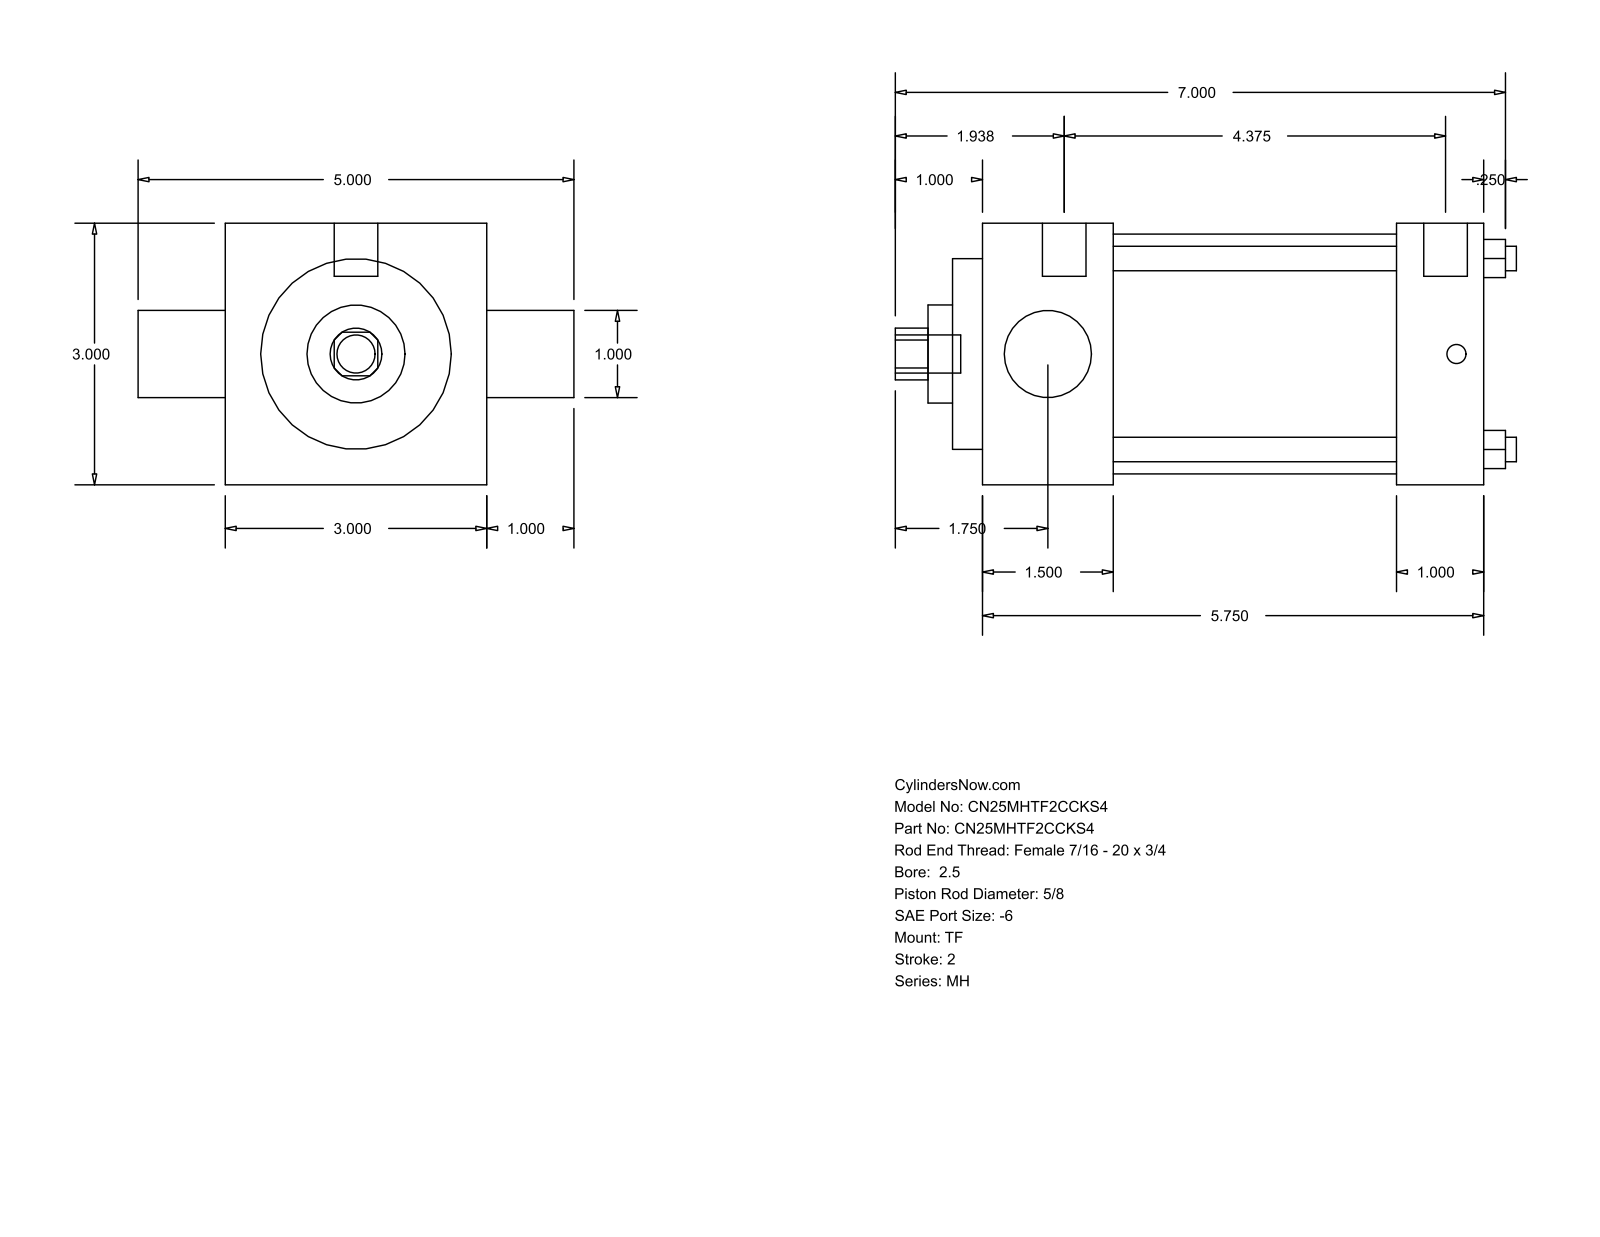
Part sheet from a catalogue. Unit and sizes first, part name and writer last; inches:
Units: inches
Overall size (bounding box): 7.125 × 5 × 3
Round holes (diameter × count): ⌀0.281 ×4, ⌀0.625 ×1, ⌀1 ×1, ⌀1.125 ×1, ⌀2.187 ×1, ⌀2.75 ×1
Round bosses / shafts (diameter × count): ⌀0.219 ×3, ⌀0.5 ×2, ⌀0.437 ×1
Partial cylindrical surfaces — rounded edges, fillets, slot ends (radius × count): R0.297 ×1
Main face-to-face distances: 3, 5.75, 1, 1.5, 4.25, 4.75, 3.25, 0.344, 1.844, 5.094
Hole centre spacings: 1.548, 2.19, 3.097
Bodies: 0 solids, 86 faces (61 planar, 25 cylindrical, 0 other)
Part name (STEP PRODUCT): MH_TF__0250_0.625
STEP written by: GSSL Pune (CONFIG_CONTROL_DESIGN)
